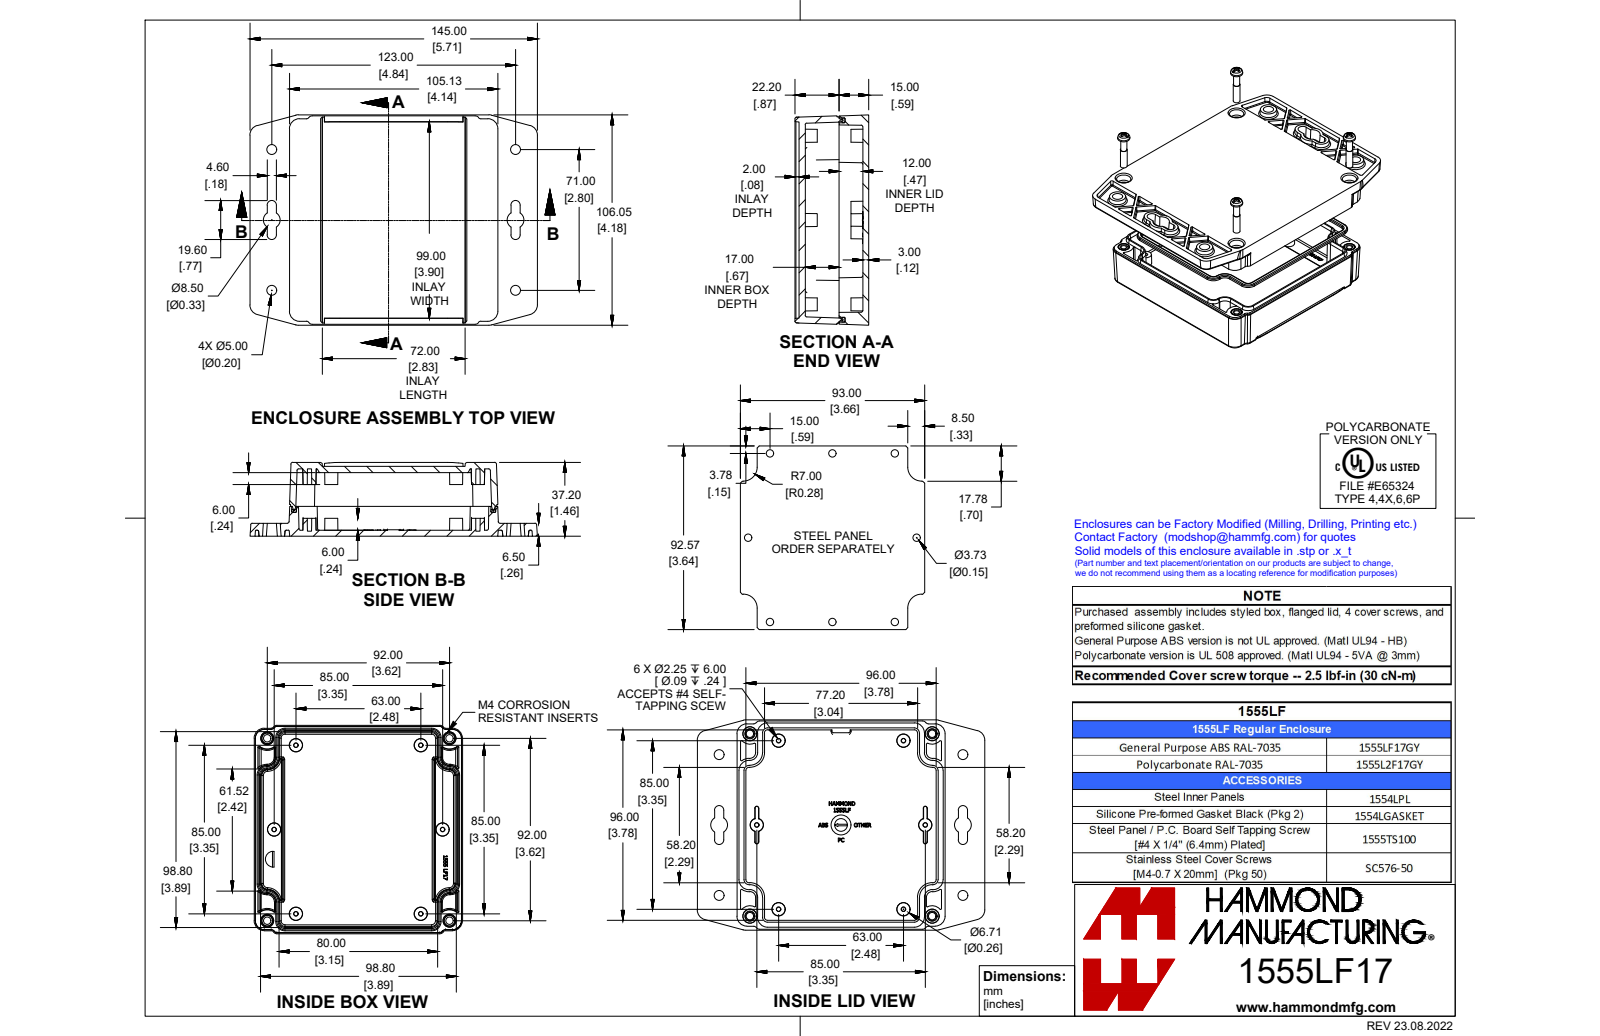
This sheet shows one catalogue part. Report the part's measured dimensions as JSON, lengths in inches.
{"part_name": "1555L2F17GY", "step_written_by": "SolidWorks 2021 (AUTOMOTIVE_DESIGN)", "units": "inches", "bodies": {"solids": 7, "faces": 1599, "planar": 453, "cylindrical": 418, "other": 728}, "overall_size": [5.709, 4.175, 1.465], "volume_in3": 8.706, "surface_area_in2": 151.3, "round_holes": [[0.128, 4], [0.223, 4]], "round_bosses_or_shafts": [[0.276, 4], [0.25, 4], [0.218, 4], [0.21, 4], [0.153, 4], [0.138, 4]], "partial_cylinders_radius": [[0.02, 114], [0.031, 48], [0.012, 16], [0.039, 8], [0.104, 8], [0.197, 8], [0.199, 8], [0.118, 4]], "face_to_face_distances": [0.126, 0.118, 1.268, 1.386, 1.142, 1.26, 0.122, 0.138, 0.256, 0.079], "hole_center_spacings": [3.622, 5.122]}
